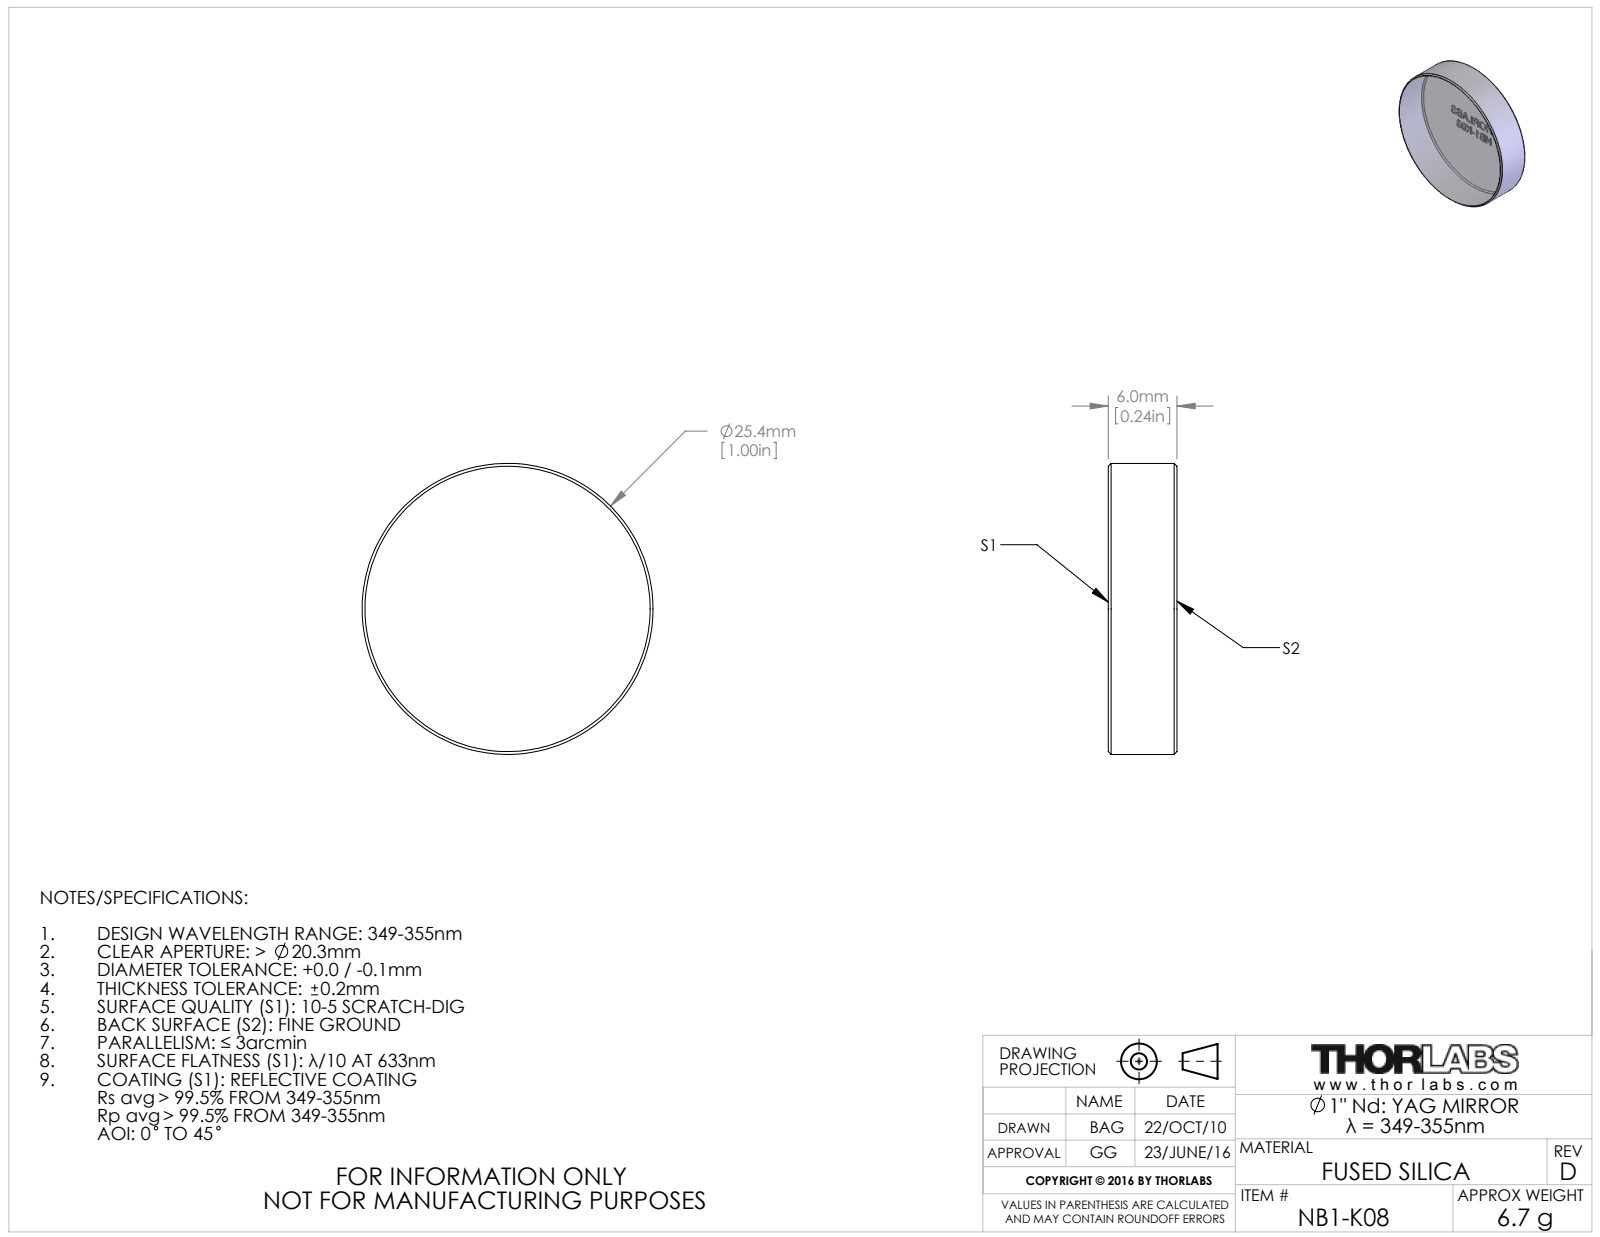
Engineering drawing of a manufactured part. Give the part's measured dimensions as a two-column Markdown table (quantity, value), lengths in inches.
| quantity | value |
| --- | --- |
| part name | 19193-E0W |
| STEP written by | SolidWorks 2016 (CONFIG_CONTROL_DESIGN) |
| units | inches |
| bodies | 1 solid, 212 faces (126 planar, 2 cylindrical, 84 other) |
| overall size | 1 × 1 × 0.236 |
| volume | 0.185 in³ |
| surface area | 2.276 in² |
| round bosses / shafts (diameter × count) | 1 × 1 |
| main face-to-face distances | 0.236, 0.061, 0.038, 0.093, 0.094, 0.122, 0.076, 0.163, 0.144, 0.043 |
